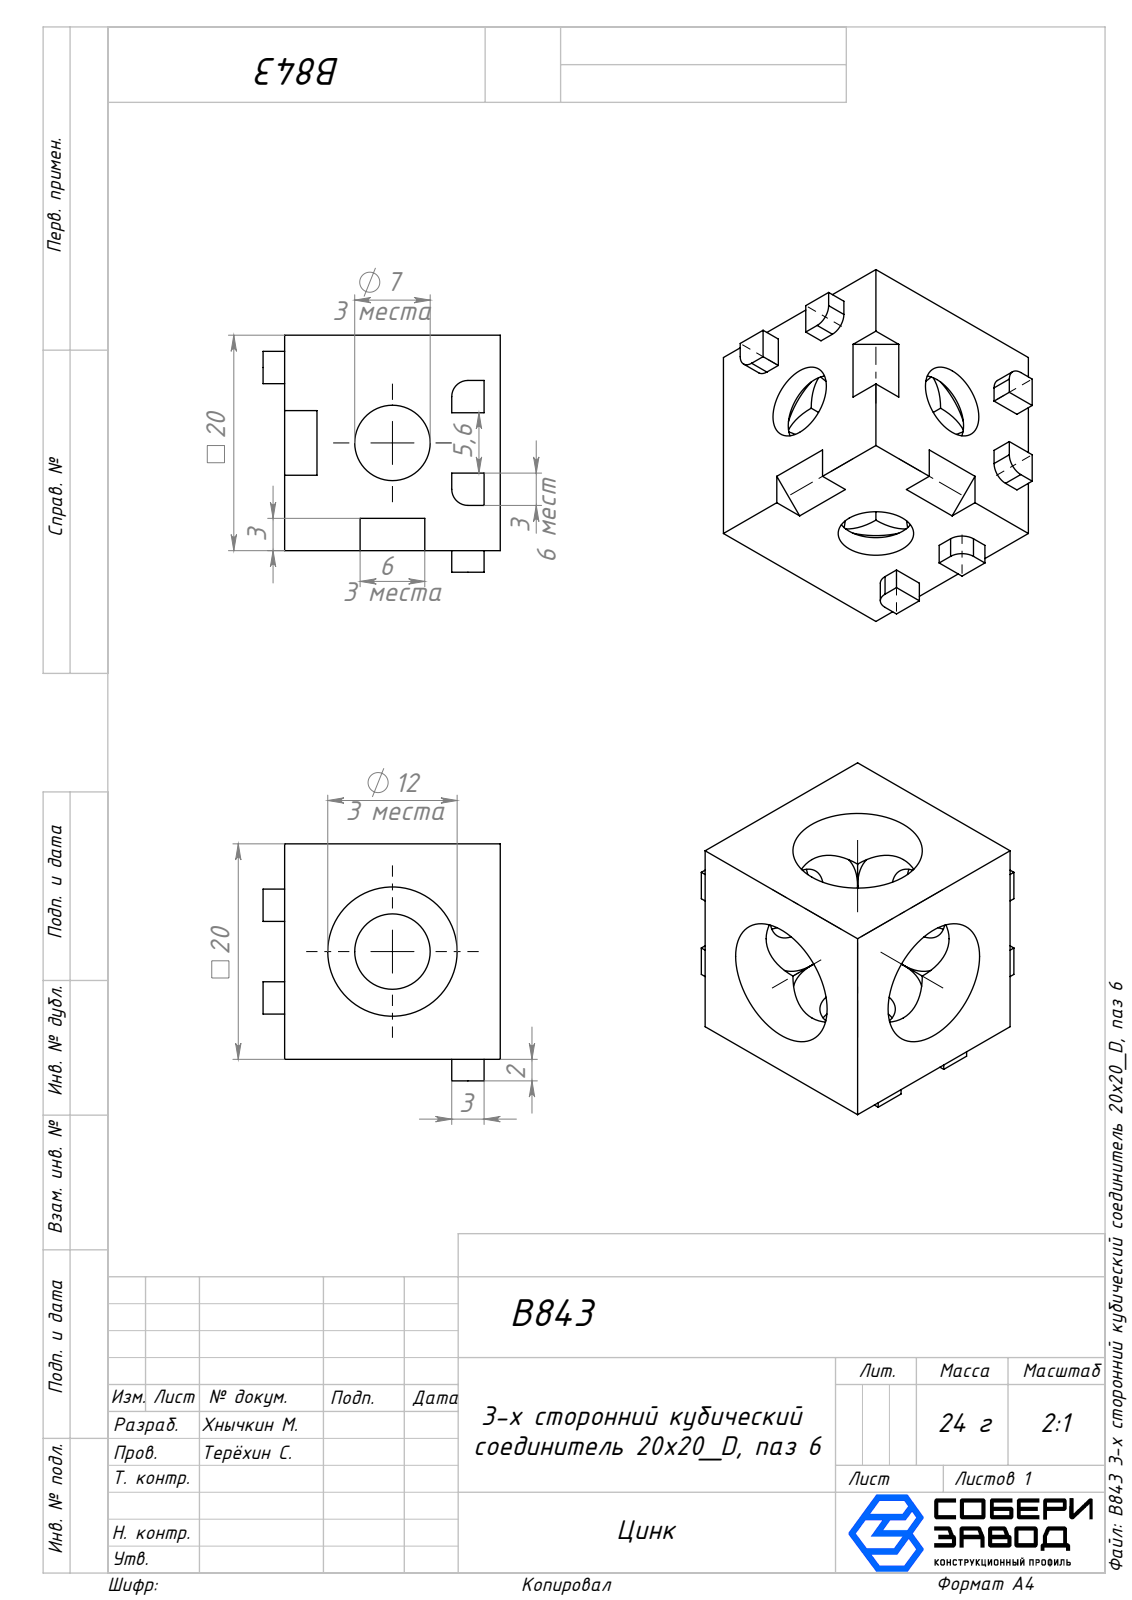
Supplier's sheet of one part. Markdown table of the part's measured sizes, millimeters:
| quantity | value |
| --- | --- |
| part name | B843 3-х сторонний кубический соединитель 20х20_D, паз 6 |
| STEP written by | SolidWorks 2025 (AUTOMOTIVE_DESIGN) |
| units | millimeters |
| bodies | 1 solid, 81 faces (45 planar, 30 cylindrical, 6 other) |
| overall size | 22 × 22 × 22 |
| volume | 4 370 mm³ |
| surface area | 3 083 mm² |
| round holes (diameter × count) | 7 × 3, 12 × 3 |
| partial cylindrical surfaces (radius × count) | 1.5 × 6 |
| main face-to-face distances | 20, 2, 22, 3, 18.5, 1.5, 7.2, 12.8, 20.5, 7 |
